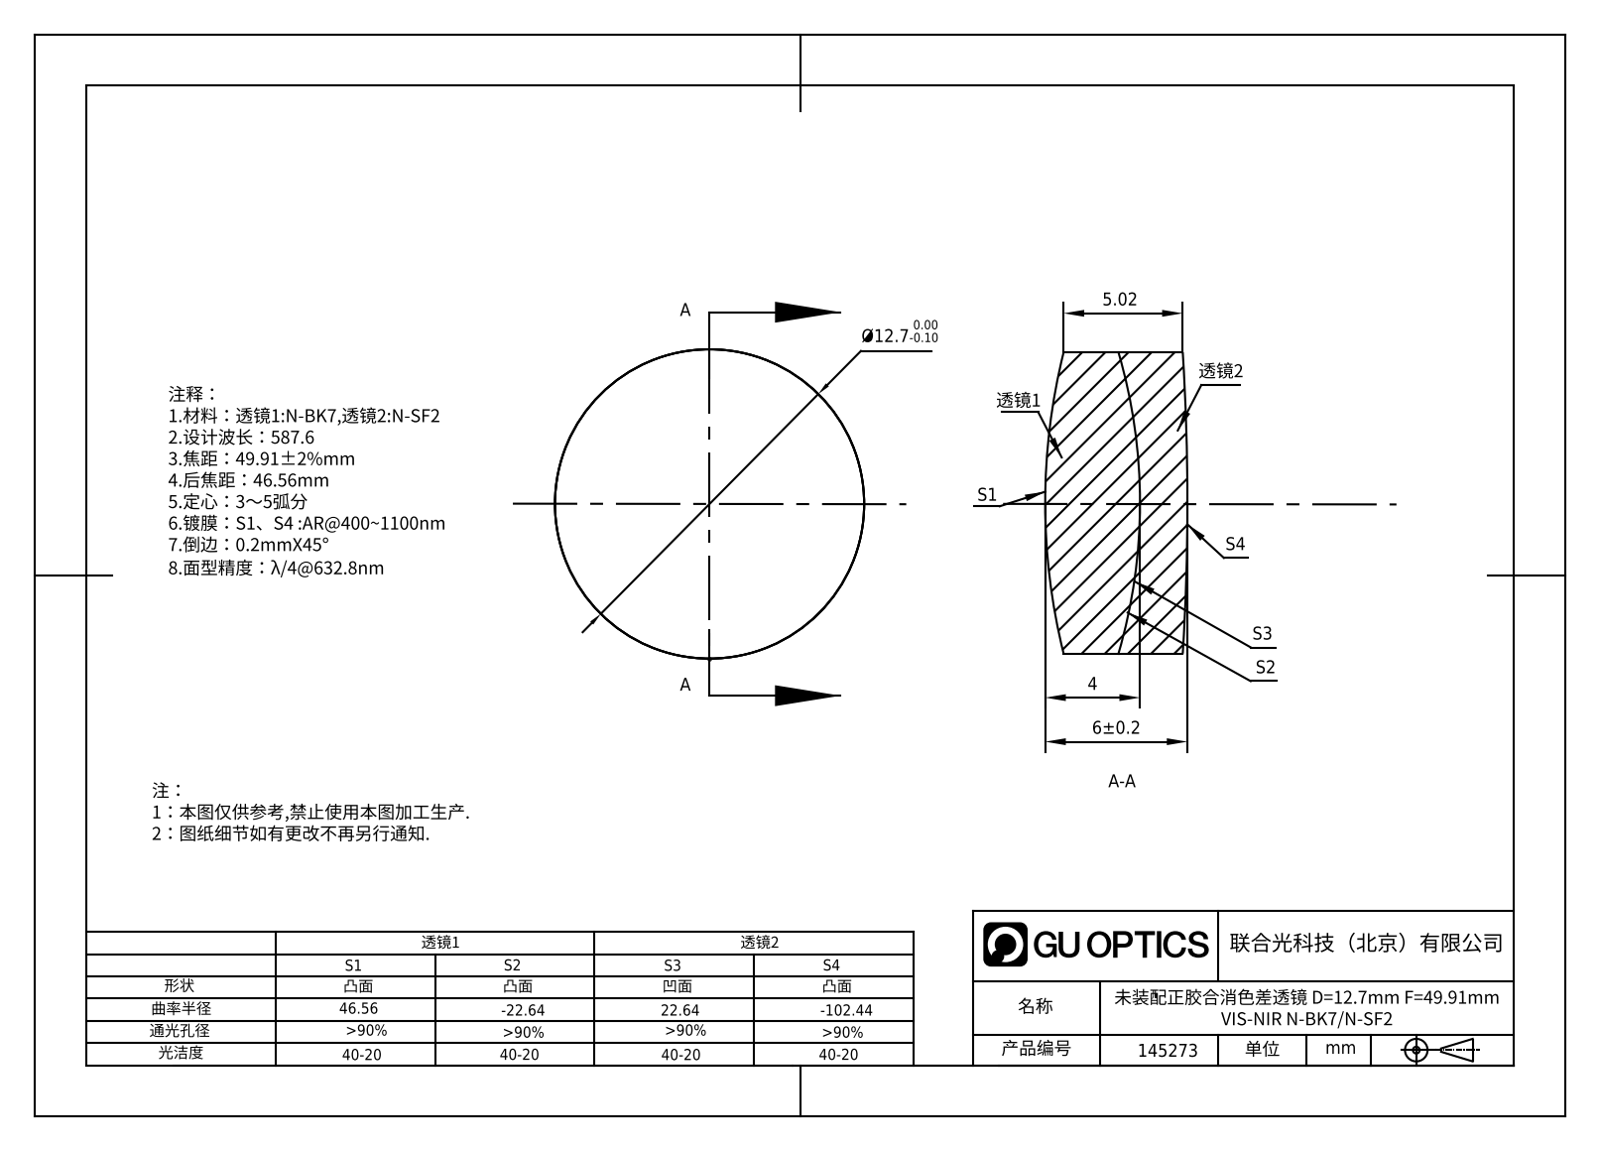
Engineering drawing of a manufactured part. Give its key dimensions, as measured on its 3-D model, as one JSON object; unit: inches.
{"part_name": "145273", "step_written_by": "SolidWorks 2020 (CONFIG_CONTROL_DESIGN)", "units": "inches", "bodies": {"solids": 2, "faces": 12, "planar": 0, "cylindrical": 4, "other": 8}, "overall_size": [0.5, 0.5, 0.236], "volume_in3": 0.043, "surface_area_in2": 1.11, "round_bosses_or_shafts": [[0.5, 1]]}
